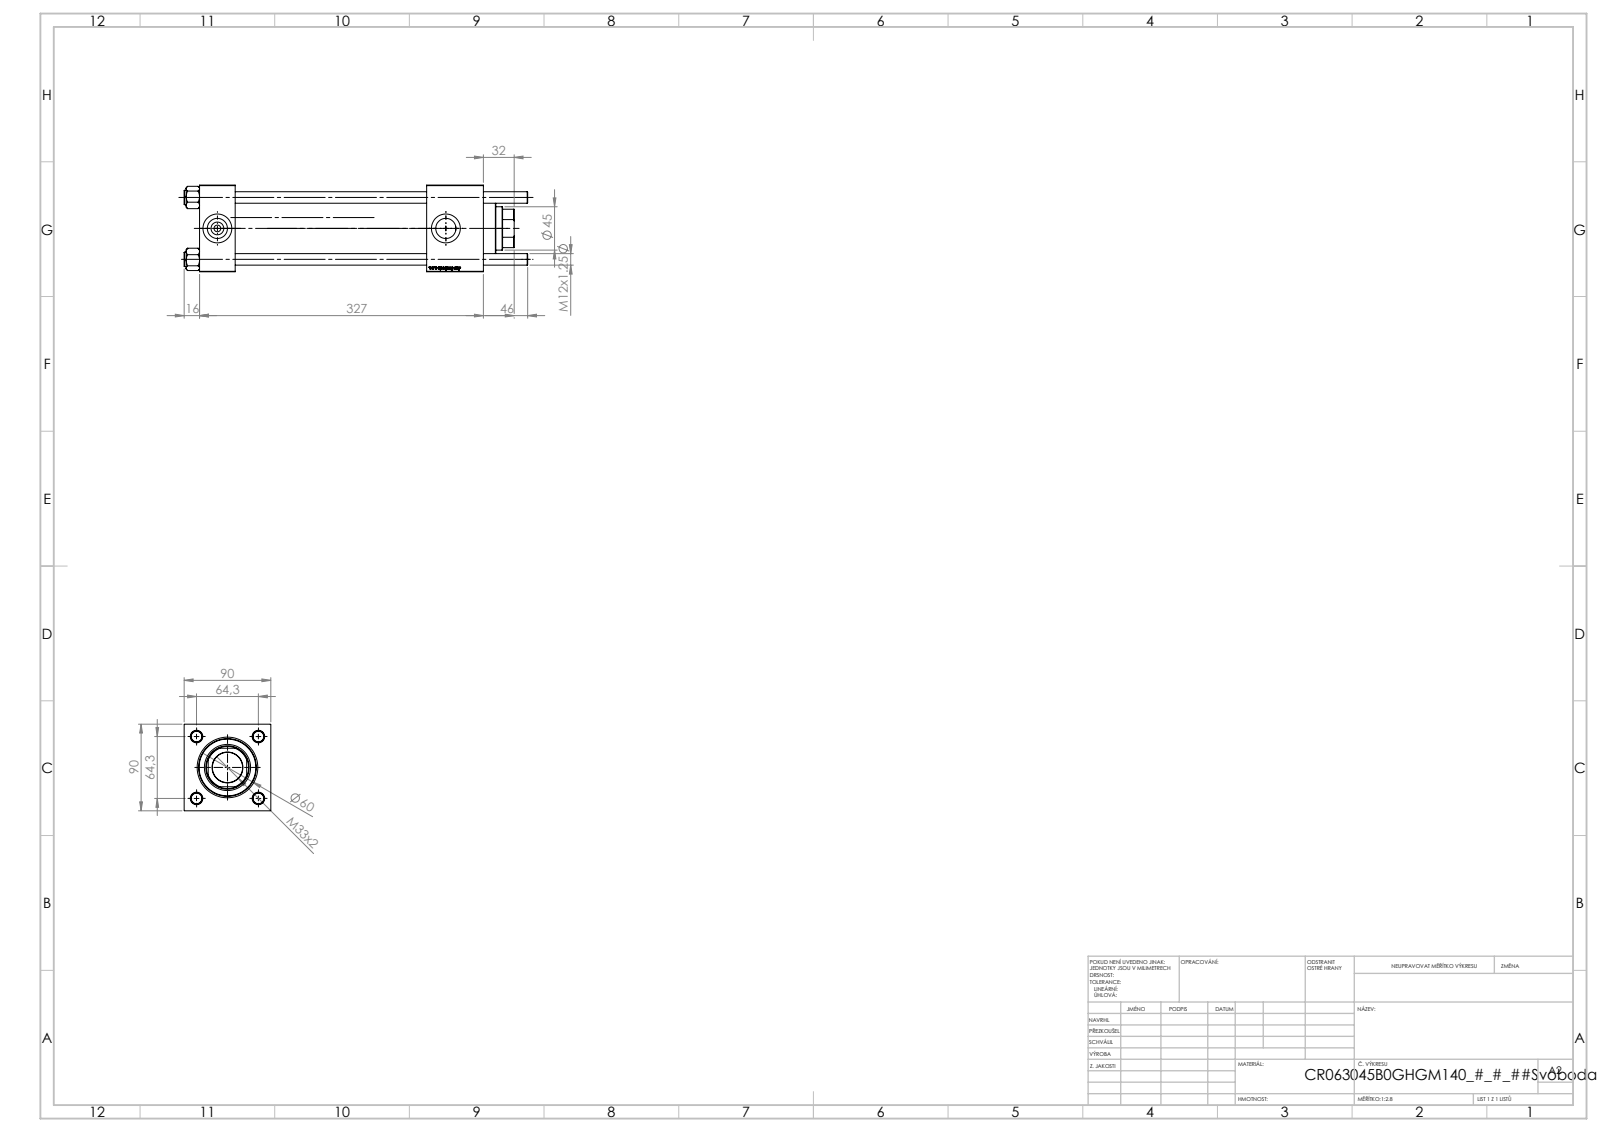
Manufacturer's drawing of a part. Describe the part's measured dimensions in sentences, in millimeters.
The part is named "V215CR_VCP_B; V215CR_B_TYCINKA; NUT_M5_B; V215CR_B-1 (+1 more)". Its 3-D file was written by "SolidWorks 2019 (CONFIG_CONTROL_DESIGN)". It is 11 solids with 1155 faces: 431 planar, 76 cylindrical and 648 other. Overall it measures 357 by 90 by 90 millimeters. Its volume is 1 406 000 cubic millimeters and its surface area 304 773 square millimeters. Round holes: 4 of diameter 12, 2 of diameter 7, 2 of diameter 20.96, 2 of diameter 30, 1 of diameter 31.5, 1 of diameter 45, 1 of diameter 48, 1 of diameter 50, 1 of diameter 60, 1 of diameter 63. Round bosses or shafts: 4 of diameter 15, 1 of diameter 69. Partial cylindrical surfaces (rounded edges, fillets, slot ends): 1 of radius 22. The main face-to-face distances are 90, 37, 236, 199, 295, 258, 59, 266.3, 229.3, 30.3. The hole center spacings are 45.47, 64.3, 90.93, 237.5.
